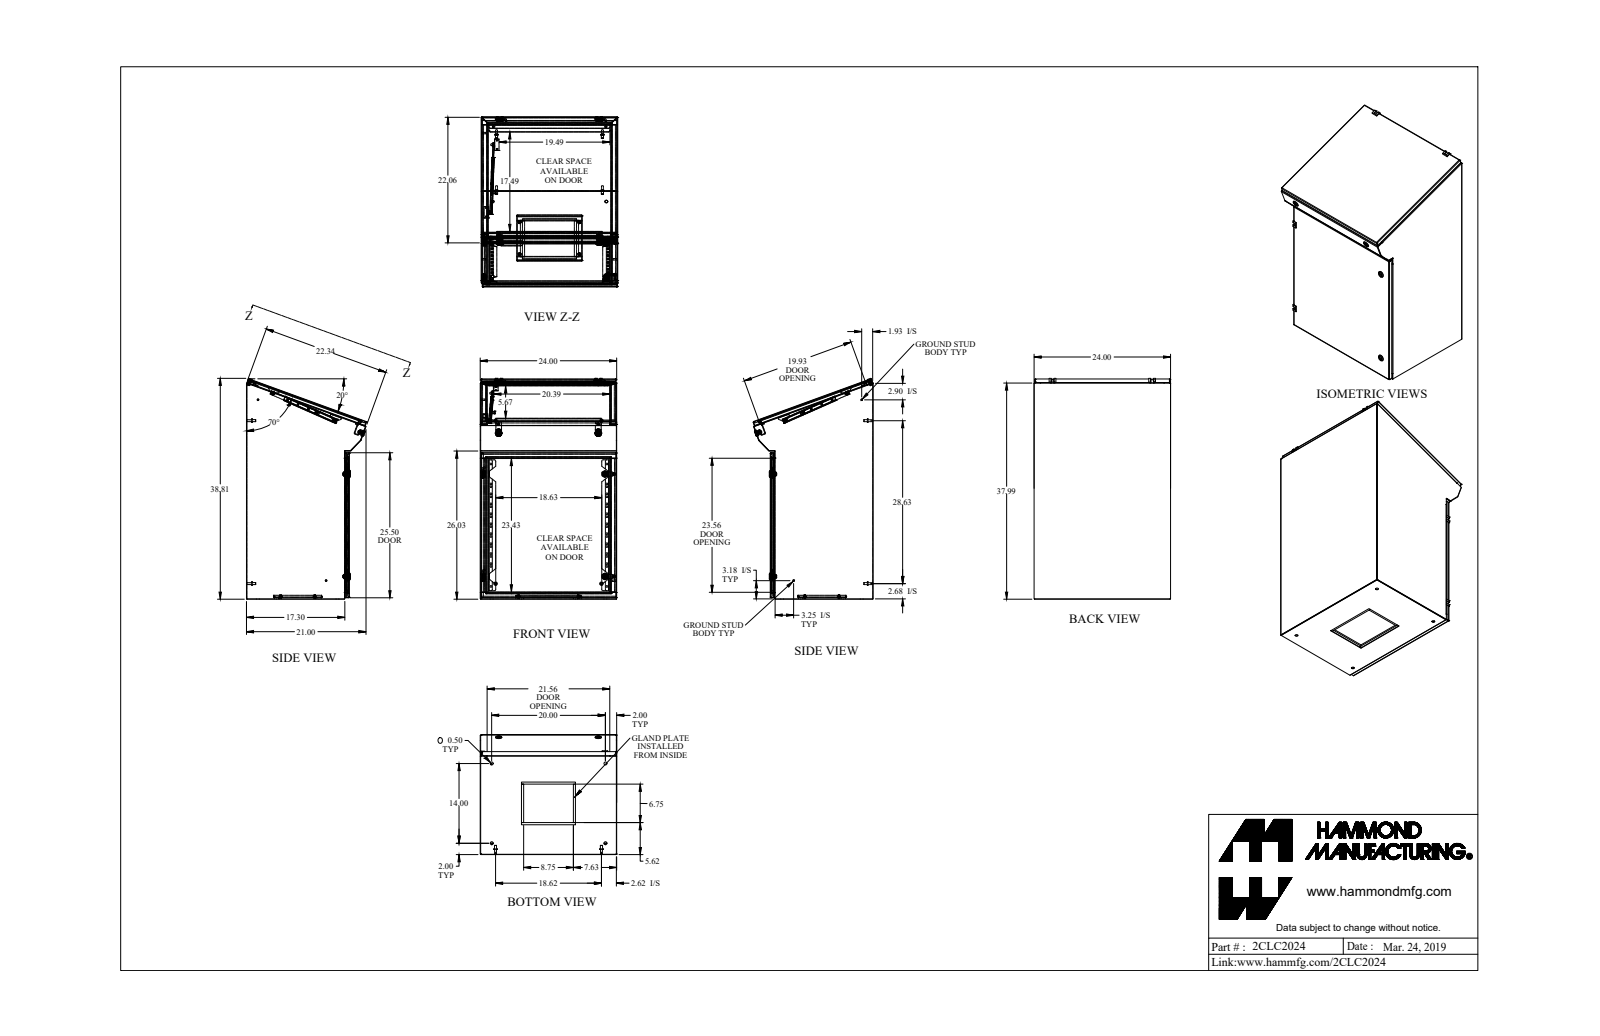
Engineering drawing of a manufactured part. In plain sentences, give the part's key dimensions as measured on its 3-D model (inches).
The part is named "2CLC2024". Its 3-D file was written by "SolidWorks 2018 (AUTOMOTIVE_DESIGN)". It is 110 solids with 1980 faces: 1335 planar, 420 cylindrical and 225 other. Overall it measures 38.742 by 24 by 21.06 inches. Its volume is 372 cubic inches and its surface area 9 642 square inches. Round holes: 45 of diameter 0.281, 6 of diameter 0.313, 5 of diameter 0.196, 4 of diameter 0.189, 4 of diameter 0.197, 4 of diameter 0.197, 4 of diameter 0.232, 4 of diameter 0.275, 4 of diameter 0.5, 4 of diameter 0.785, 3 of diameter 0.25, 2 of diameter 0.272. Round bosses or shafts: 10 of diameter 0.236, 8 of diameter 0.25, 6 of diameter 0.281, 6 of diameter 0.226, 5 of diameter 0.5, 4 of diameter 1.1, 4 of diameter 0.65, 4 of diameter 0.625. Partial cylindrical surfaces (rounded edges, fillets, slot ends): 48 of radius 0.036, 48 of radius 0.108, 24 of radius 0.125, 12 of radius 0.25, 6 of radius 0.043, 6 of radius 0.375, 4 of radius 0.047, 4 of radius 0.312. The main face-to-face distances are 0.072, 18.015, 23.928, 17.943, 23.856, 24, 18.087, 0.322, 0.25, 0.787. The hole center spacings are 1.75, 17.5, 3.5, 5.25, 7, 0.5, 4, 8.75.
